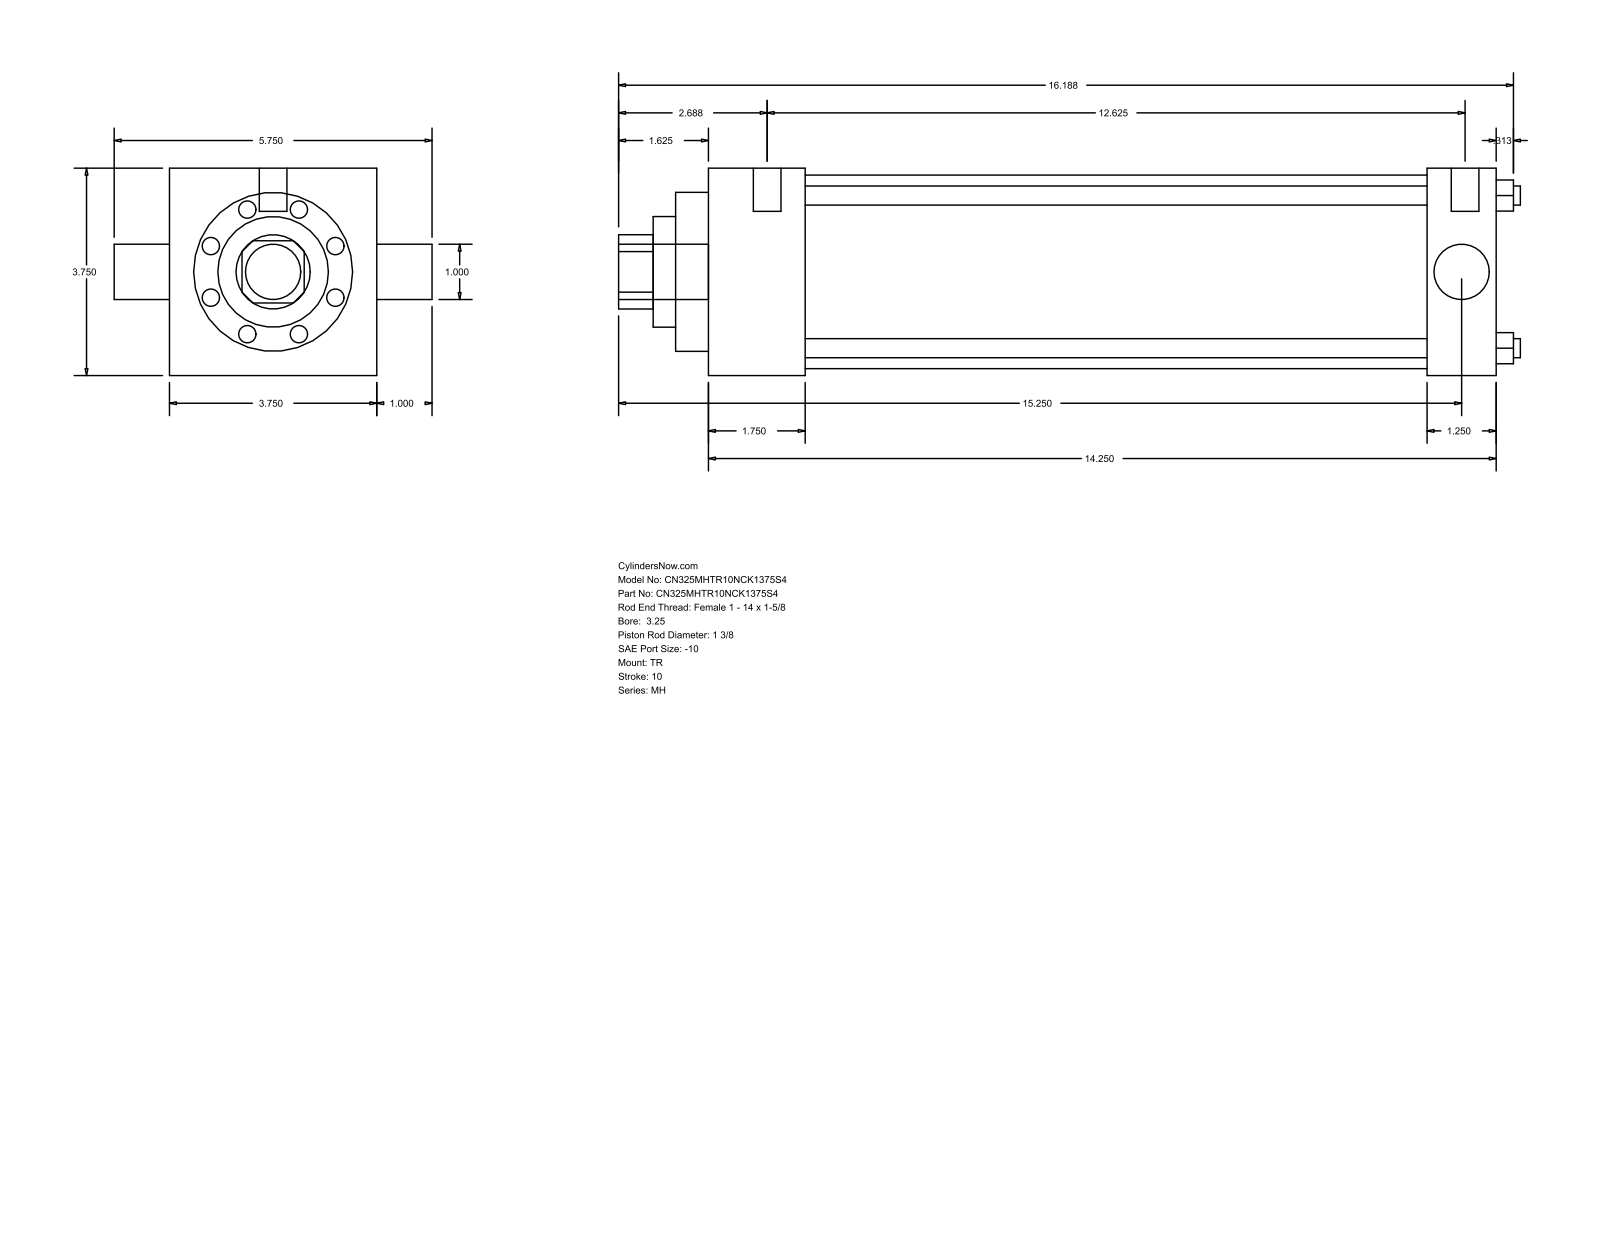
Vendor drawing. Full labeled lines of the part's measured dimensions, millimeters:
Part name (STEP PRODUCT): MH_TR__0325_1.375
STEP written by: GSSL Pune (CONFIG_CONTROL_DESIGN)
Units: millimetres
Bodies: 0 solids, 86 faces (61 planar, 25 cylindrical, 0 other)
Overall size (bounding box): 414.34 × 146.05 × 95.25
Round holes (diameter × count): ⌀8.76 ×4, ⌀25.4 ×1, ⌀34.92 ×1, ⌀50.8 ×1, ⌀73.03 ×1, ⌀88.9 ×1
Round bosses / shafts (diameter × count): ⌀5.56 ×3, ⌀12.7 ×2, ⌀25.4 ×1
Partial cylindrical surfaces — rounded edges, fillets, slot ends (radius × count): R17.06 ×1
Main face-to-face distances: 95.24, 361.96, 44.45, 330.21, 285.76, 317.51, 31.75, 15.08, 59.53, 345.29
Hole centre spacings: 49.57, 70.1, 99.14
